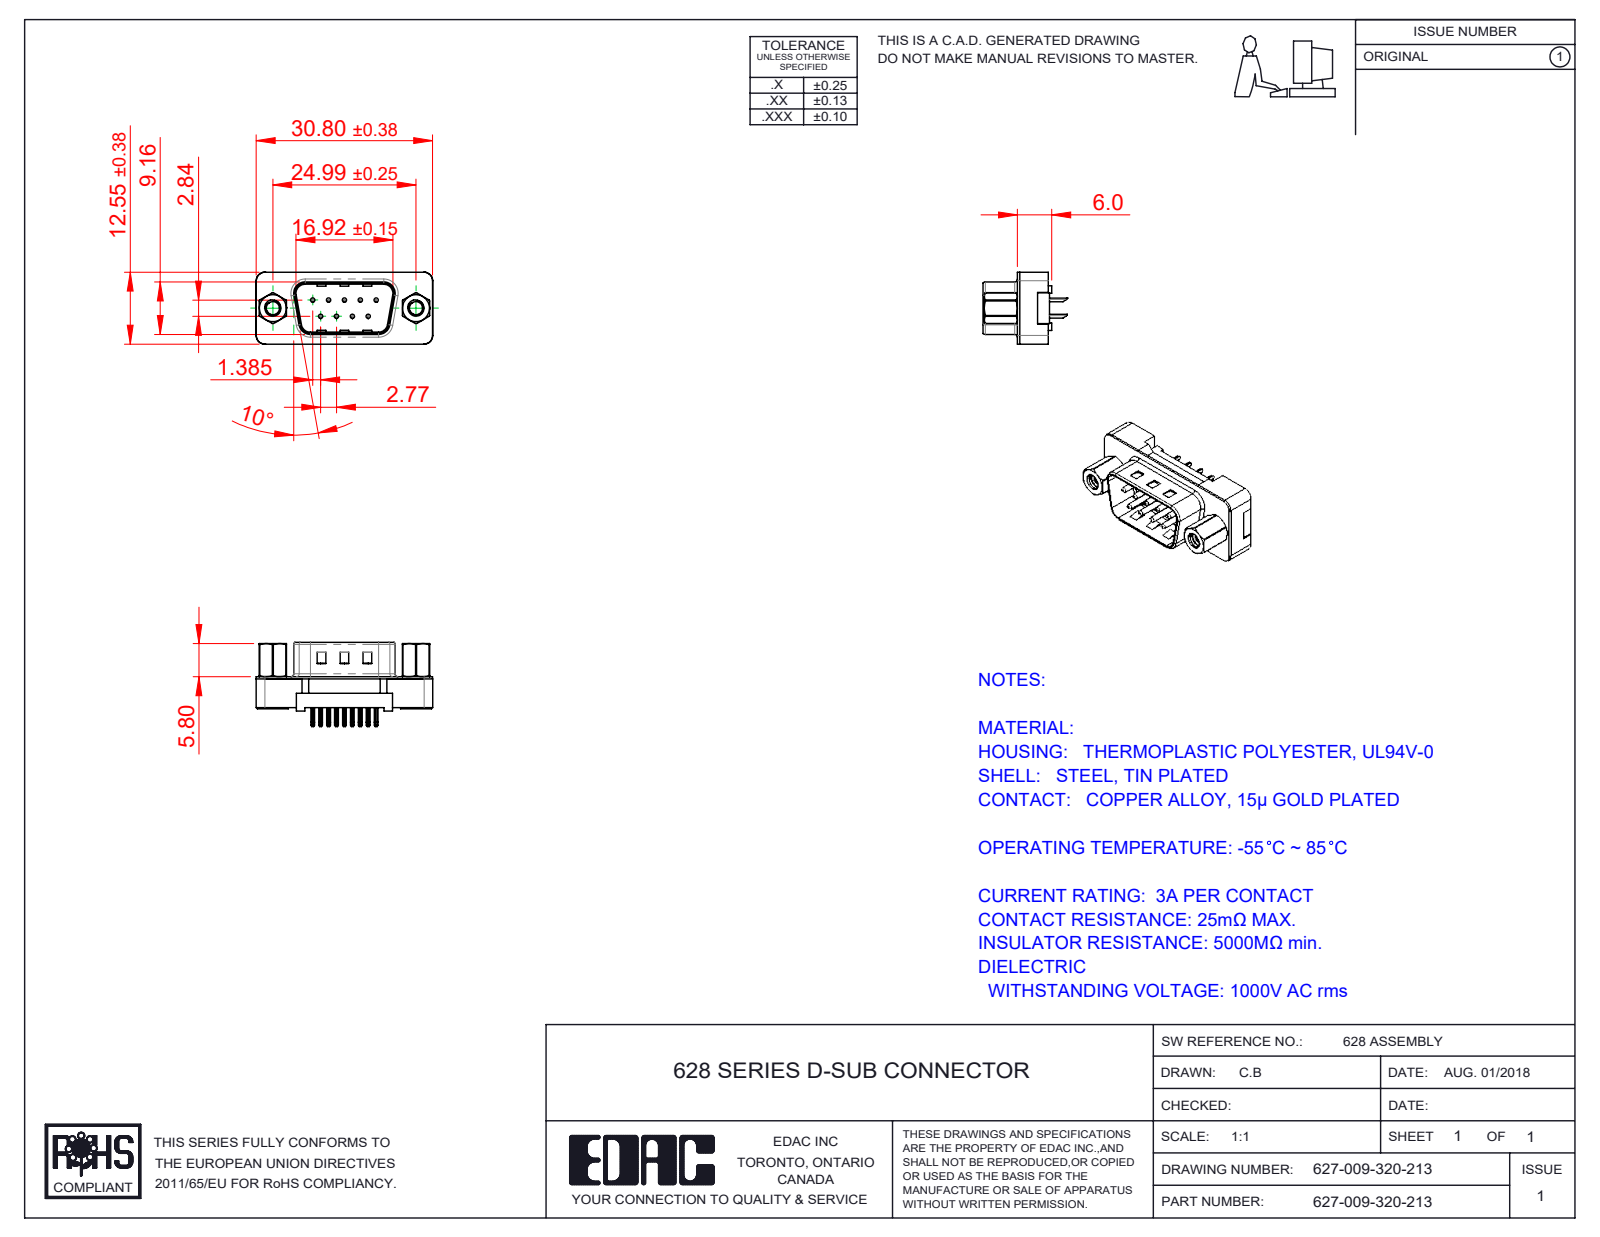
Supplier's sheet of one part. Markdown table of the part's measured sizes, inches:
| quantity | value |
| --- | --- |
| part name | 627 4-40 Hex Standoff; 627 PB Shell_09 Contacts; 627-009-320-213; 627 PB Contact Row 1_20 (+3 more) |
| STEP written by | SolidWorks 2020 (CONFIG_CONTROL_DESIGN) |
| units | inches |
| bodies | 15 solids, 909 faces (503 planar, 312 cylindrical, 94 other) |
| overall size | 1.213 × 0.579 × 0.494 |
| volume | 0.113 in³ |
| surface area | 5.954 in² |
| round holes (diameter × count) | 0.014 × 9, 0.033 × 9, 0.089 × 2, 0.09 × 2, 0.157 × 2, 0.189 × 2, 0.197 × 2 |
| round bosses / shafts (diameter × count) | 0.03 × 9, 0.193 × 2, 0.11 × 2 |
| partial cylindrical surfaces (radius × count) | 0.01 × 18, 0.005 × 9, 0.02 × 8, 0.059 × 7, 0.035 × 4, 0.063 × 4, 0.079 × 4, 0.016 × 2 |
| main face-to-face distances | 0.016, 0.098, 0.213, 0.197, 0.114, 0.345, 0.083, 0.256, 0.027, 0.334 |
| hole center spacings | 0.124, 0.109, 0.198, 0.218, 0.295, 0.198, 0.279, 0.327 |
